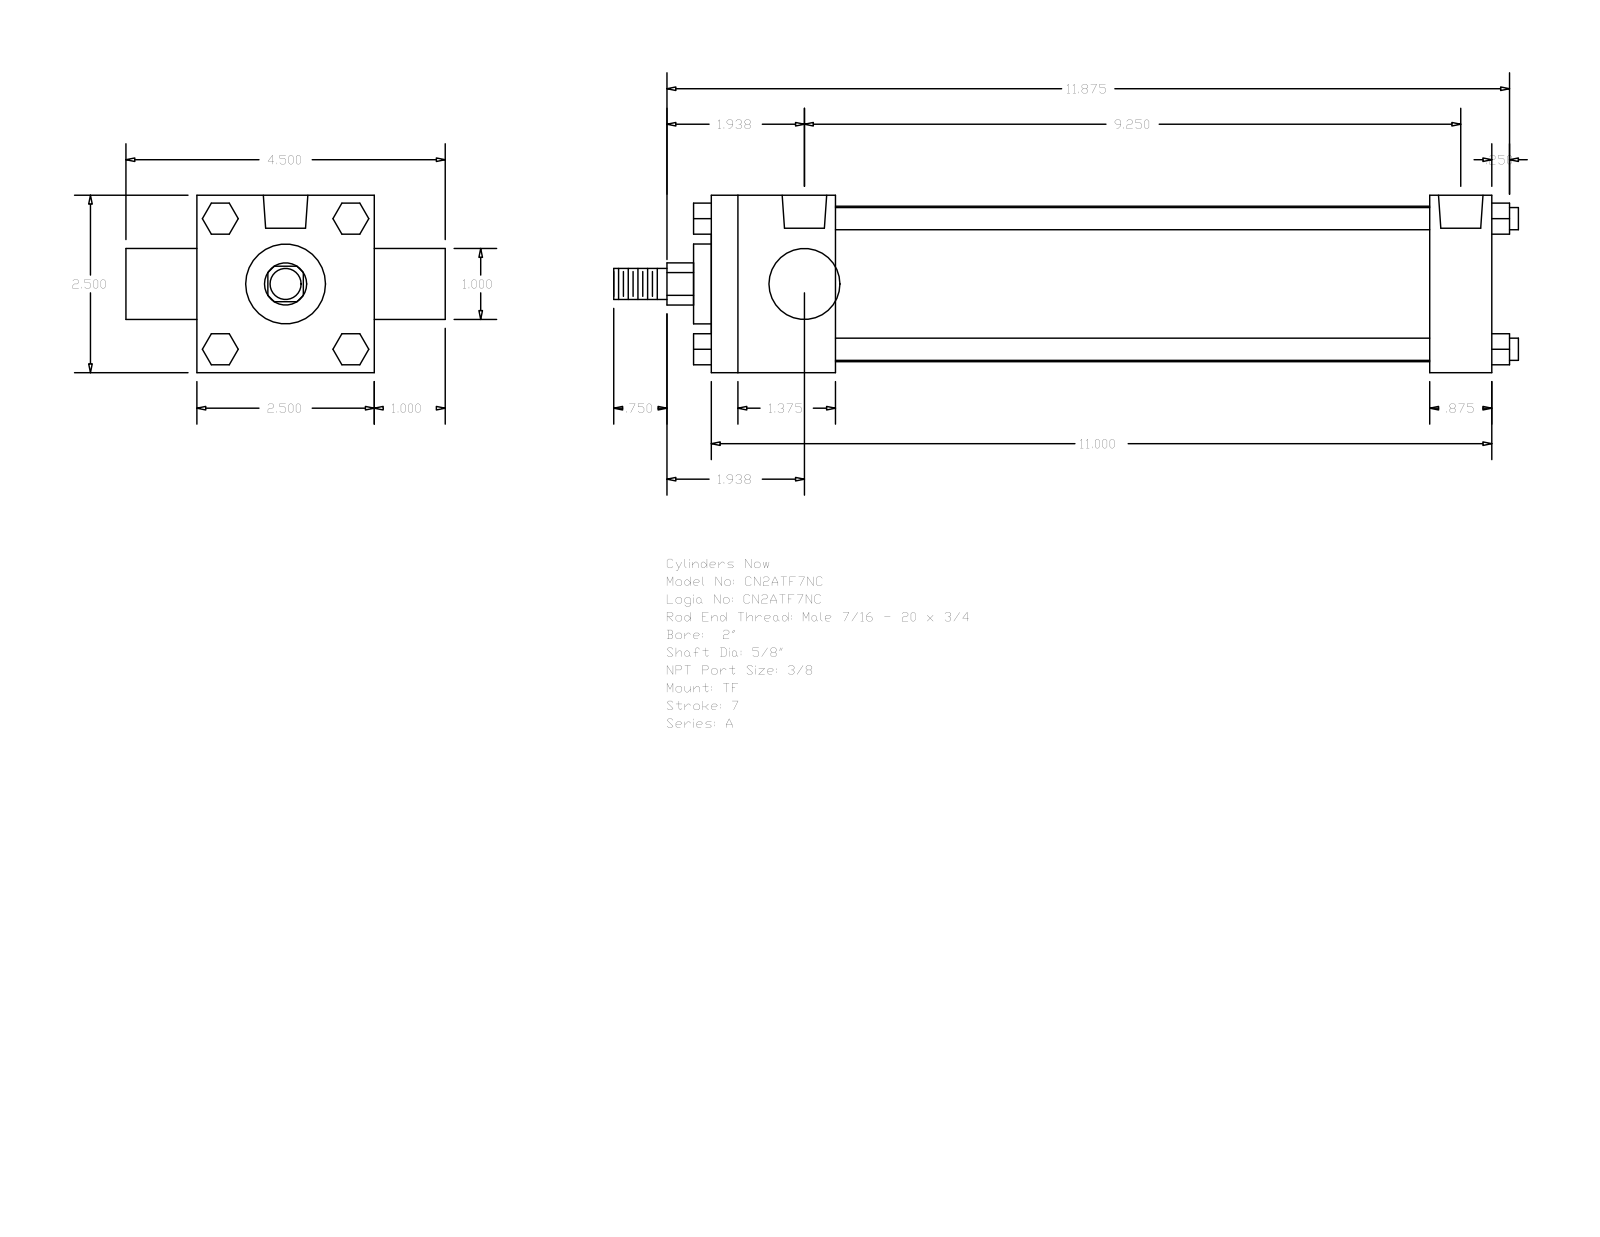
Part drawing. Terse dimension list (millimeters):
name: A_TF__0200_0.625
written by: GSSL Pune (CONFIG_CONTROL_DESIGN)
unit: mm
bodies: 0 solids, 120 faces (92 planar, 28 cylindrical, 0 other)
size: 323.85 × 114.3 × 63.5
holes: 3× ⌀5.56, 2× ⌀15.93
bosses: 4× ⌀7.94, 1× ⌀55.63, 1× ⌀28.57, 1× ⌀25.4, 1× ⌀15.88, 1× ⌀11.11
rounds: 1× R7.54
face distances: 63.5, 279.39, 44.45, 257.17, 212.72, 234.94, 22.22, 25.4, 88.9, 6.35
hole spacings: 3.97, 3.98, 227, 230.97, 230.98, 234.95
